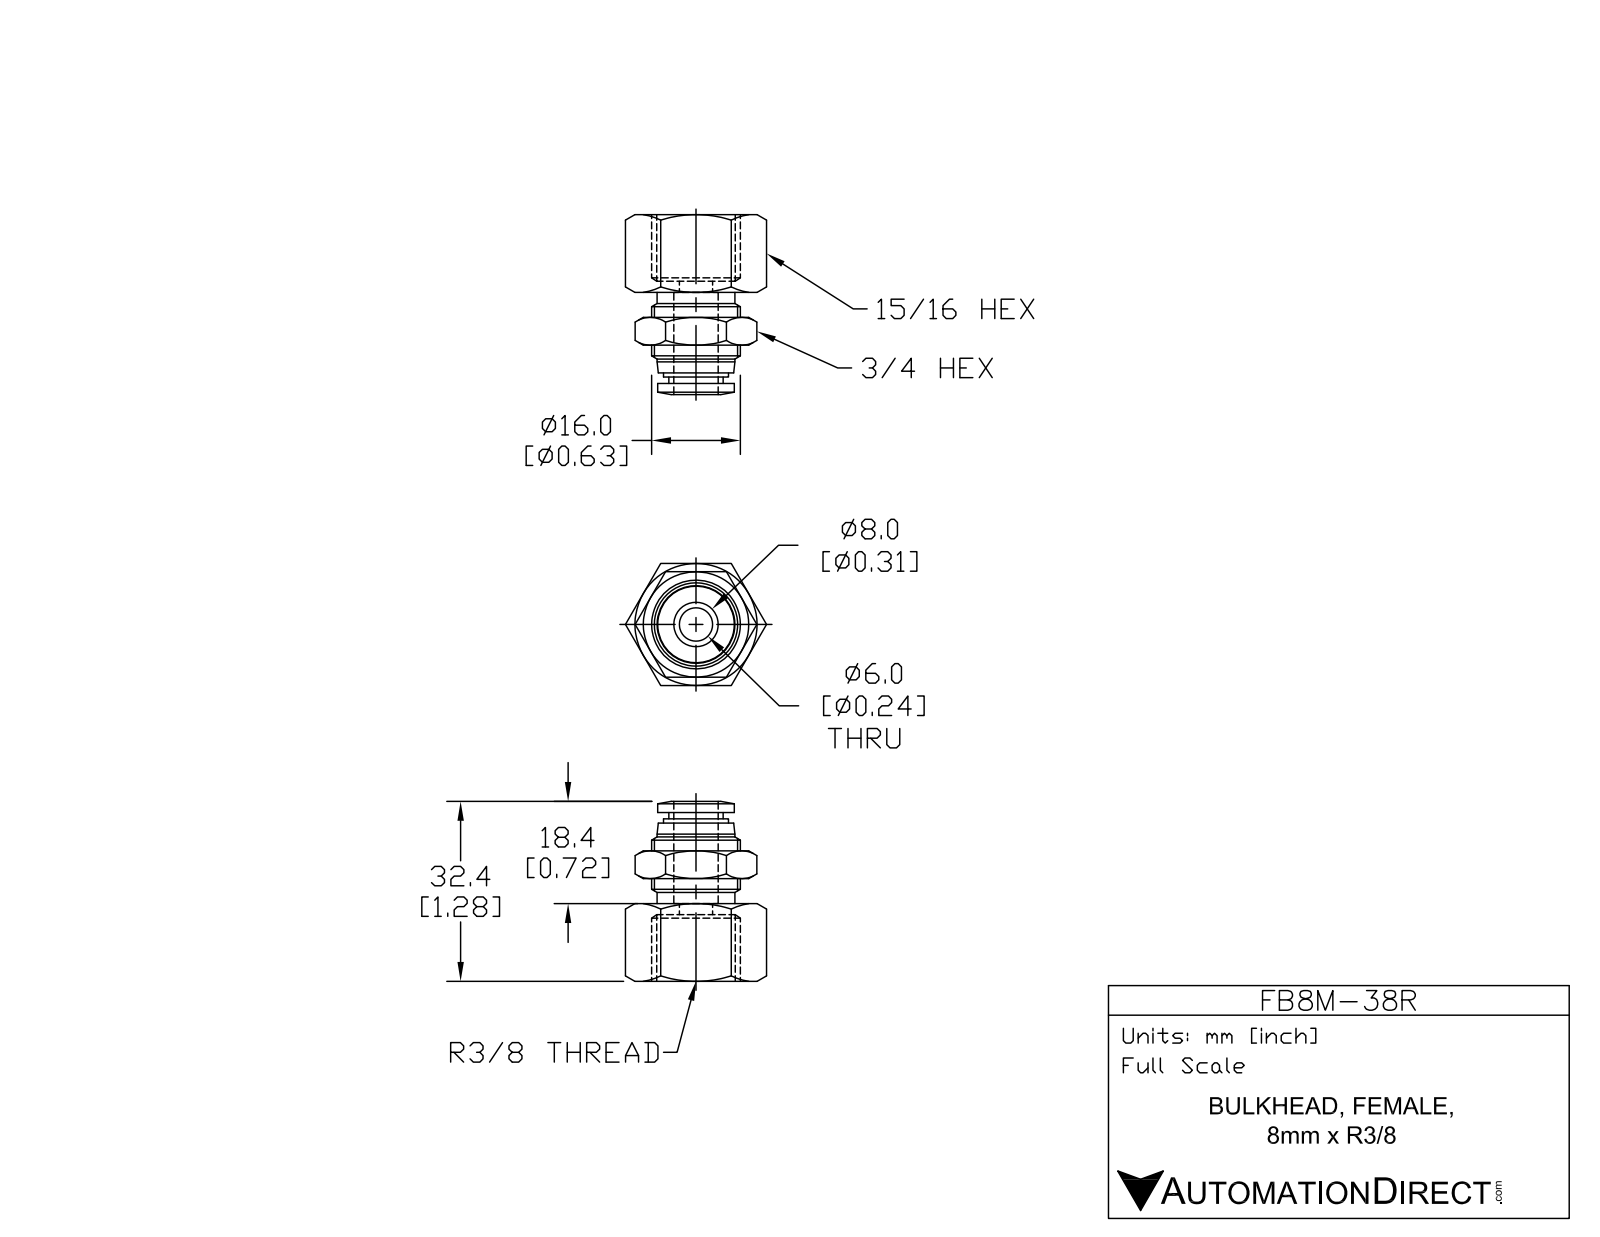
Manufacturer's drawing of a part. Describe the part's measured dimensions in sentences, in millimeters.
The part is named "FB8M-38R". Its 3-D file was written by "SolidWorks 2015 (AUTOMOTIVE_DESIGN)". It is 1 solid with 80 faces: 22 planar, 18 cylindrical and 40 other. Overall it measures 32.4 by 25.4 by 22 millimeters. Its volume is 5 950 cubic millimeters and its surface area 4 214 square millimeters. Round holes: 1 of diameter 6, 1 of diameter 8.3. Round bosses or shafts: 1 of diameter 16, 1 of diameter 14, 1 of diameter 13.8, 1 of diameter 11.7, 1 of diameter 9.8. The main face-to-face distances are 22, 20.5, 1.5, 2, 12, 14, 19, 18.2, 6.2, 4.2.
